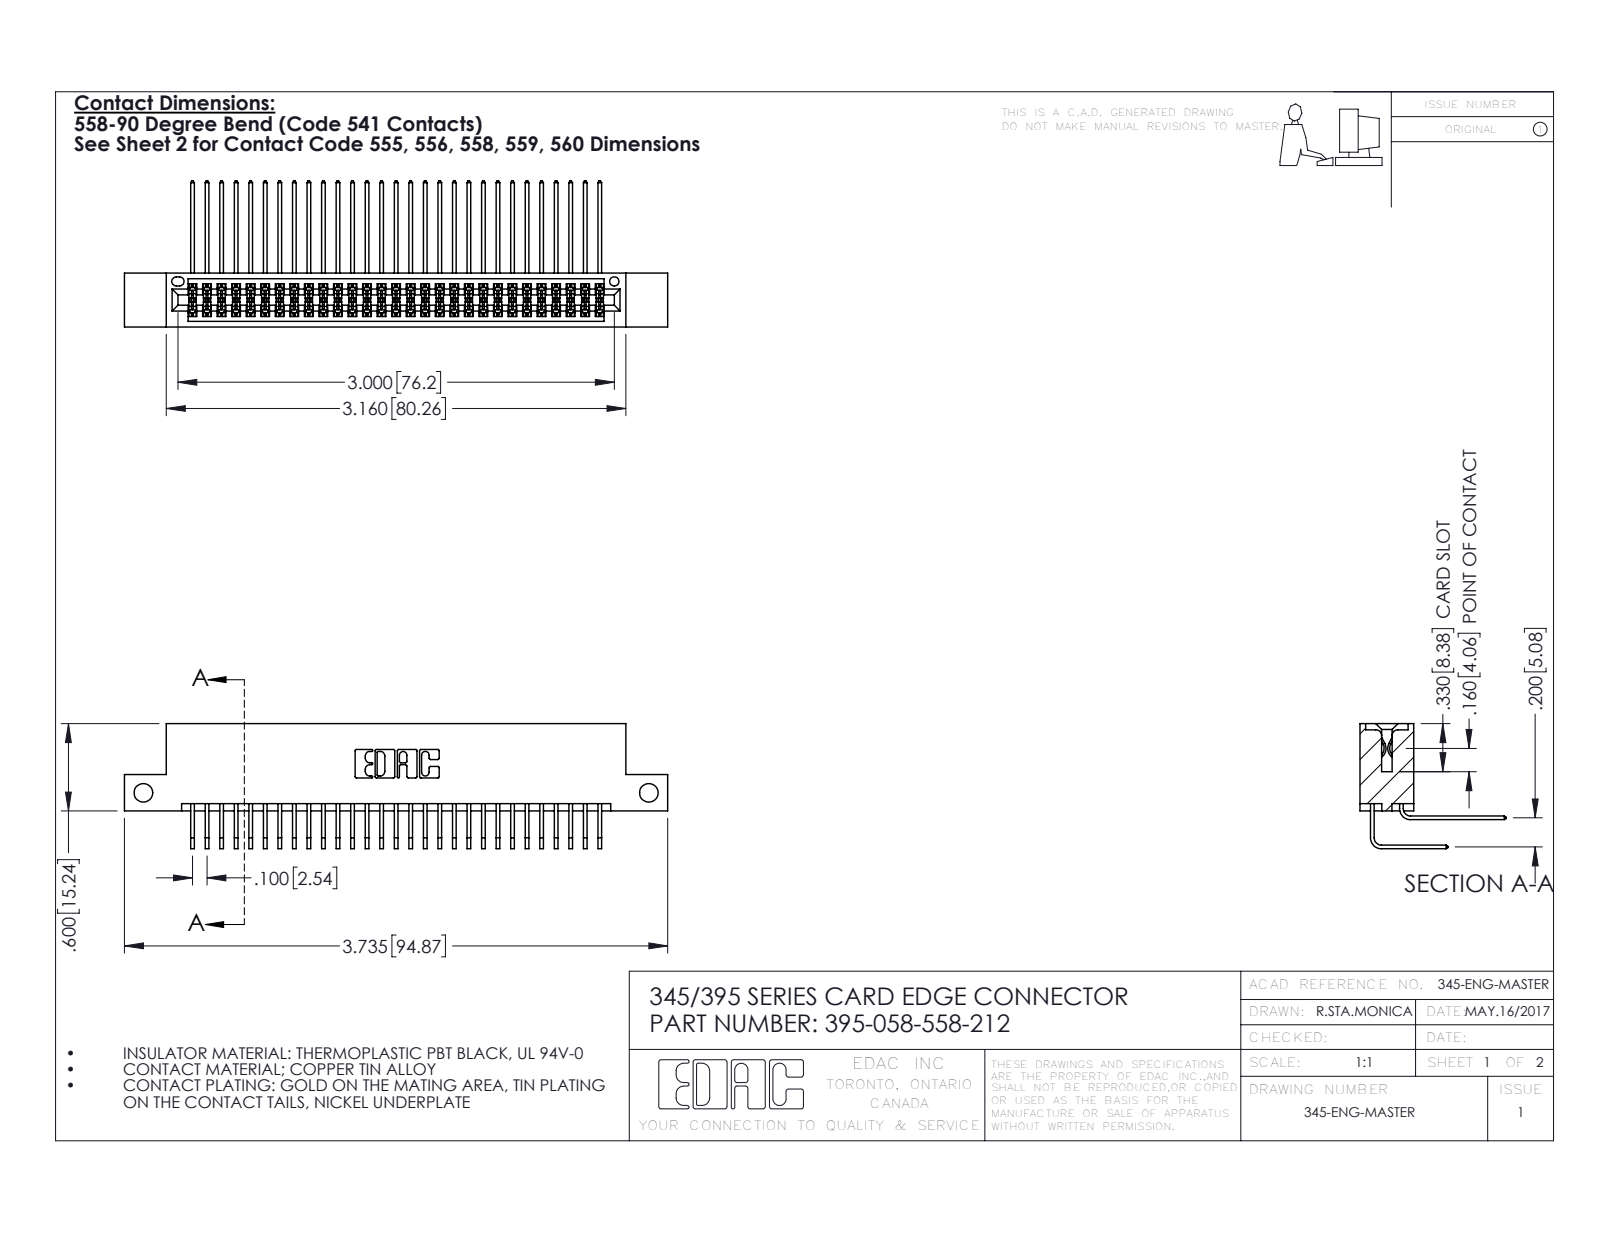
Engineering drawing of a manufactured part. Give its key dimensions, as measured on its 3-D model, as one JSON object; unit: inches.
{"part_name": "345-292-001_558 Tail - 2; 345-292-001_558 559 Tail - 1; 345 Part_Flush Mounting Lugs - Side Mount; 395-058-558-212", "step_written_by": "SolidWorks 2016 (CONFIG_CONTROL_DESIGN)", "units": "inches", "bodies": {"solids": 59, "faces": 3142, "planar": 2110, "cylindrical": 1032, "other": 0}, "overall_size": [3.735, 1.005, 0.859], "volume_in3": 0.57, "surface_area_in2": 23.24, "round_holes": [[0.128, 2], [0.064, 1]], "partial_cylinders_radius": [[0.006, 88], [0.01, 22], [0.007, 6], [0.031, 6], [0.026, 3], [0.014, 2], [0.019, 2], [0.022, 2]], "face_to_face_distances": [0.2, 0.072, 0.298, 0.37, 0.098, 0.272, 0.025, 0.225, 0.285, 0.025], "hole_center_spacings": [3.475]}
